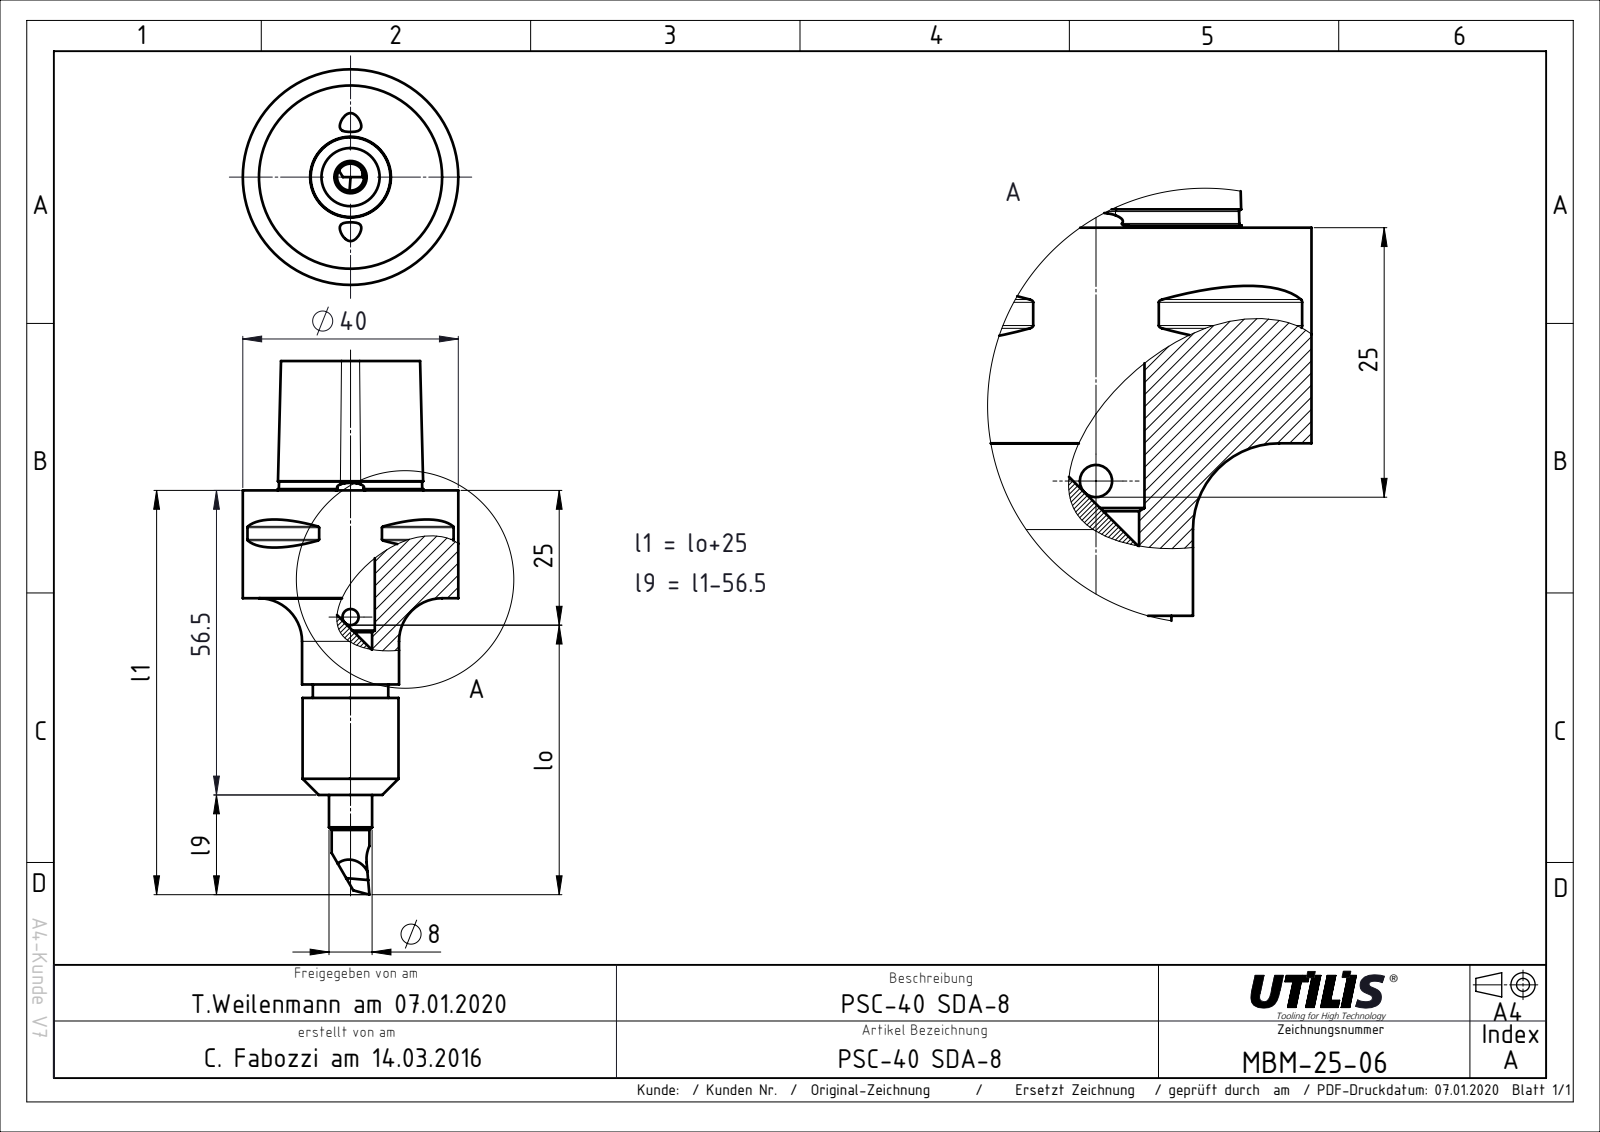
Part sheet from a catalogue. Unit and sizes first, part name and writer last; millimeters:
Units: millimetres
Overall size (bounding box): 99 × 40 × 40
Round holes (diameter × count): ⌀4.6 ×1, ⌀18 ×1, ⌀20 ×1
Round bosses / shafts (diameter × count): ⌀40 ×1, ⌀34 ×1, ⌀17.8 ×1, ⌀14 ×1, ⌀8 ×1
Partial cylindrical surfaces — rounded edges, fillets, slot ends (radius × count): R0.3 ×8, R3 ×1, R3.5 ×1
Main face-to-face distances: 20, 24, 44, 15.51, 60, 36, 16, 62.5, 38.5, 18.5
Volume: 45 058 mm³ · Surface area: 10 066 mm²
Bodies: 1 solid, 129 faces (28 planar, 29 cylindrical, 72 other)
Part name (STEP PRODUCT): MBM-25 PSC40_SDA8
STEP written by: SolidWorks 2015 (AUTOMOTIVE_DESIGN)
